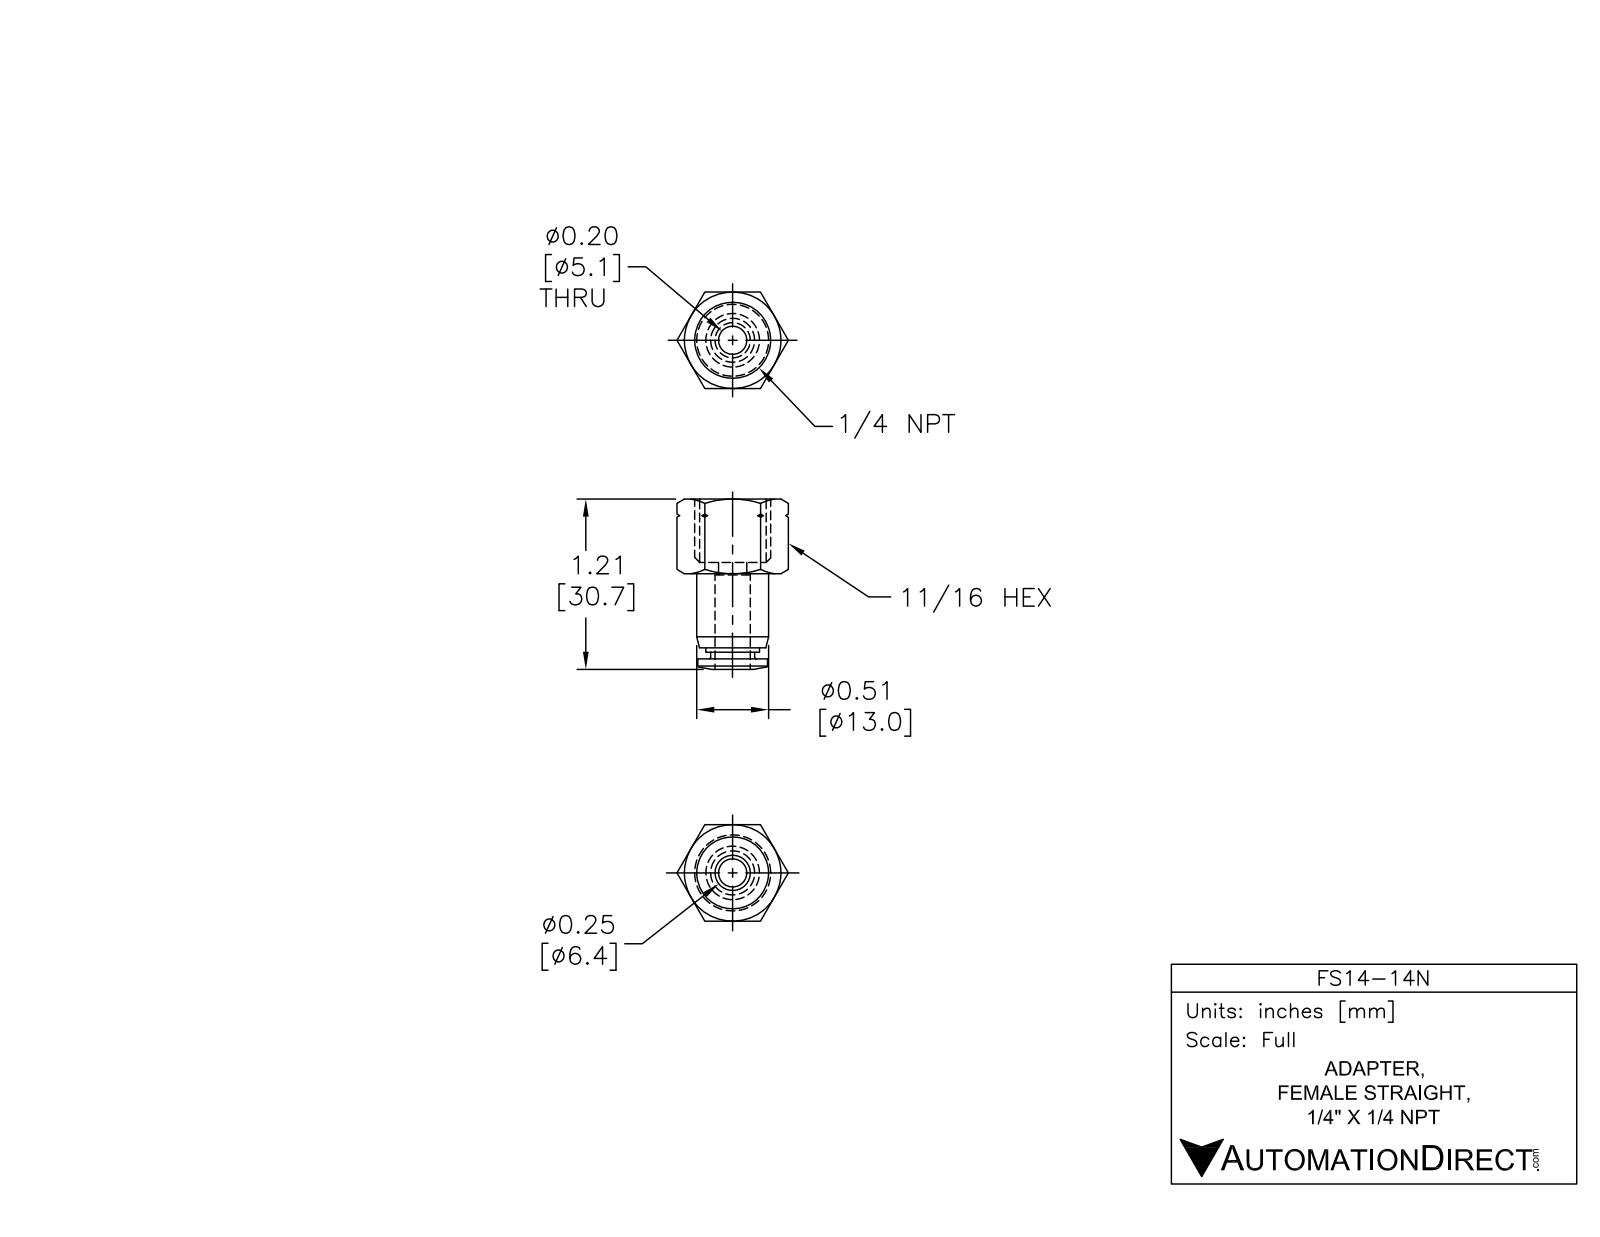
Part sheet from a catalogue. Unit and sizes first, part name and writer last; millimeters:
Units: millimetres
Overall size (bounding box): 30.8 × 20.2 × 17.4
Round holes (diameter × count): ⌀5 ×1, ⌀6.6 ×1
Round bosses / shafts (diameter × count): ⌀13 ×1, ⌀12.6 ×1, ⌀9.7 ×1, ⌀8 ×1
Main face-to-face distances: 17.4, 2, 15.4, 11.5, 13.5, 28.9, 17.4, 26.9, 13.4, 27.7
Volume: 3 410 mm³ · Surface area: 2 916 mm²
Bodies: 1 solid, 63 faces (13 planar, 12 cylindrical, 38 other)
Part name (STEP PRODUCT): FS14-14N
STEP written by: SolidWorks 2015 (AUTOMOTIVE_DESIGN)
